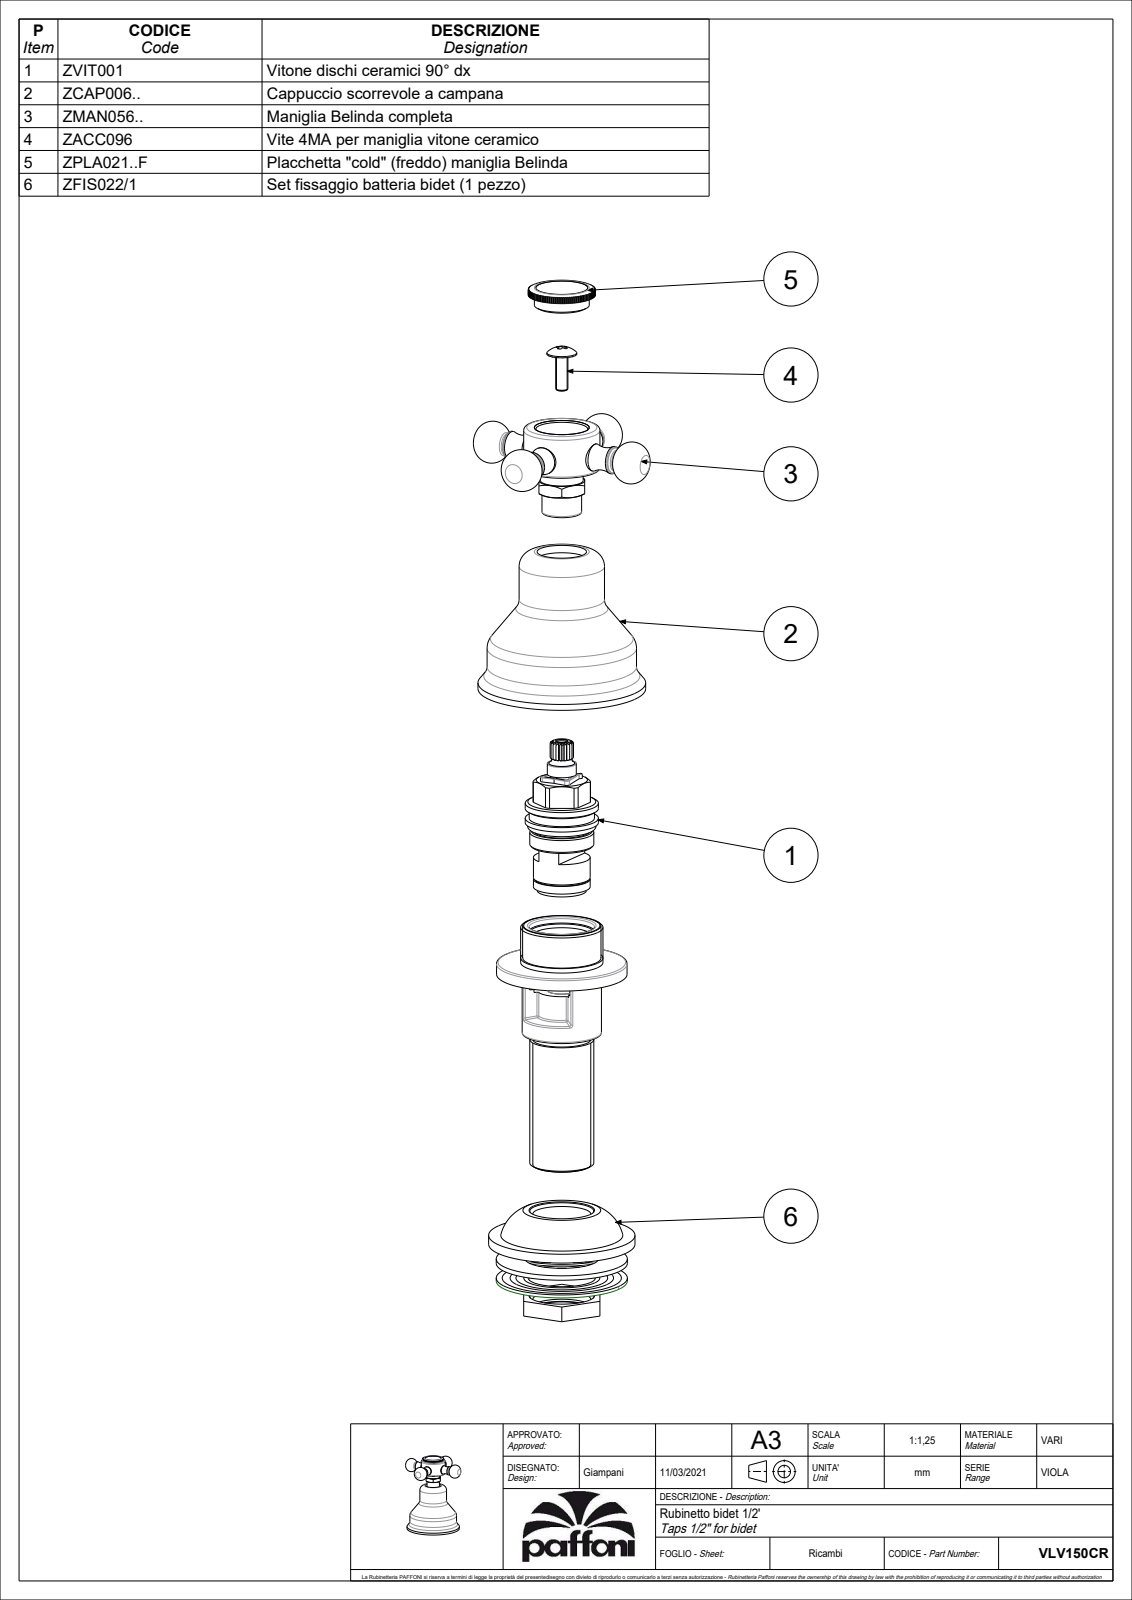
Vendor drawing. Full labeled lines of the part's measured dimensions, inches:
Part name (STEP PRODUCT): VLV150CR
STEP written by: CREO PARAMETRIC BY PTC INC, 2020044 (CONFIG_CONTROL_DESIGN)
Units: inches
Bodies: 1 solid, 435 faces (217 planar, 138 cylindrical, 80 other)
Overall size (bounding box): 3.008 × 2.522 × 2.522
Volume: 4.492 in³ · Surface area: 22.24 in²
Round bosses / shafts (diameter × count): ⌀0.354 ×2, ⌀0.276 ×2, ⌀2.165 ×1, ⌀1.929 ×1, ⌀1.102 ×1, ⌀0.984 ×1, ⌀0.551 ×1, ⌀0.512 ×1
Partial cylindrical surfaces — rounded edges, fillets, slot ends (radius × count): R0.433 ×1
Main face-to-face distances: 2.35, 1.831, 0.52, 0.591, 0.598, 0.157, 2.035, 0.205, 0.315, 2.902
